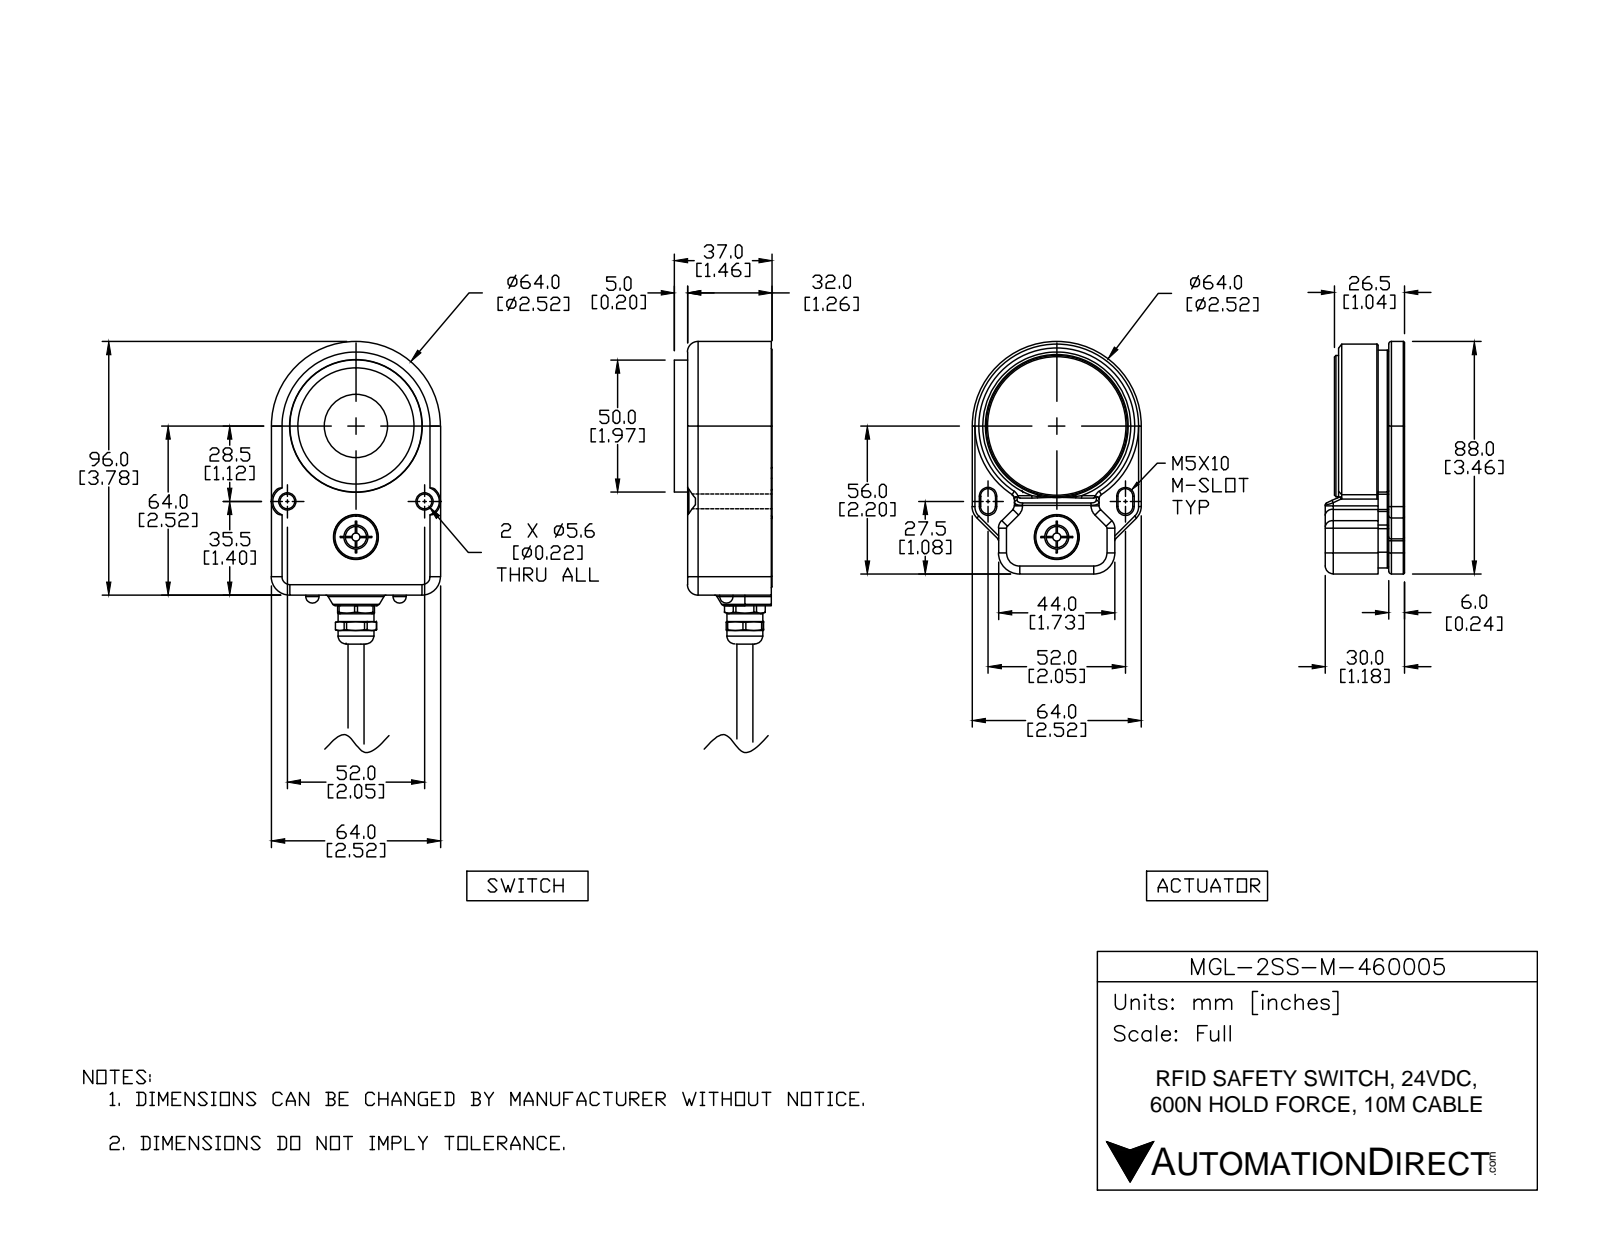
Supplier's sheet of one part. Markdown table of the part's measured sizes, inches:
| quantity | value |
| --- | --- |
| part name | MGL-2SS-M-460005; MGL-2SS-M-460005_2; MGL-2SS-M-460005_1 |
| STEP written by | SolidWorks 2017 (AUTOMOTIVE_DESIGN) |
| units | inches |
| bodies | 20 solids, 1740 faces (445 planar, 724 cylindrical, 571 other) |
| overall size | 7.717 × 2.539 × 2.52 |
| volume | 12.53 in³ |
| surface area | 169.9 in² |
| round holes (diameter × count) | 0.098 × 8, 0.157 × 8, 0.13 × 6, 0.315 × 6, 0.197 × 5, 0.354 × 3, 0.22 × 2, 0.413 × 2, 0.669 × 2, 0.252 × 1, 0.264 × 1, 0.268 × 1 |
| round bosses / shafts (diameter × count) | 0.02 × 4, 0.236 × 2, 0.228 × 2, 0.22 × 2, 0.118 × 2, 2.441 × 1, 2.26 × 1, 2.102 × 1 |
| partial cylindrical surfaces (radius × count) | 0.02 × 218, 0.039 × 69, 0.079 × 30, 0.012 × 17, 0.118 × 15, 0.157 × 12, 0.236 × 8, 0.024 × 7 |
| main face-to-face distances | 0.098, 0.236, 0.413, 0.118, 1.89, 0.748, 1.043, 0.394, 1.142, 0.079 |
| hole center spacings | 0.706, 0.768, 1.086, 1.024, 2.147, 0.346, 0.376, 0.382 |
